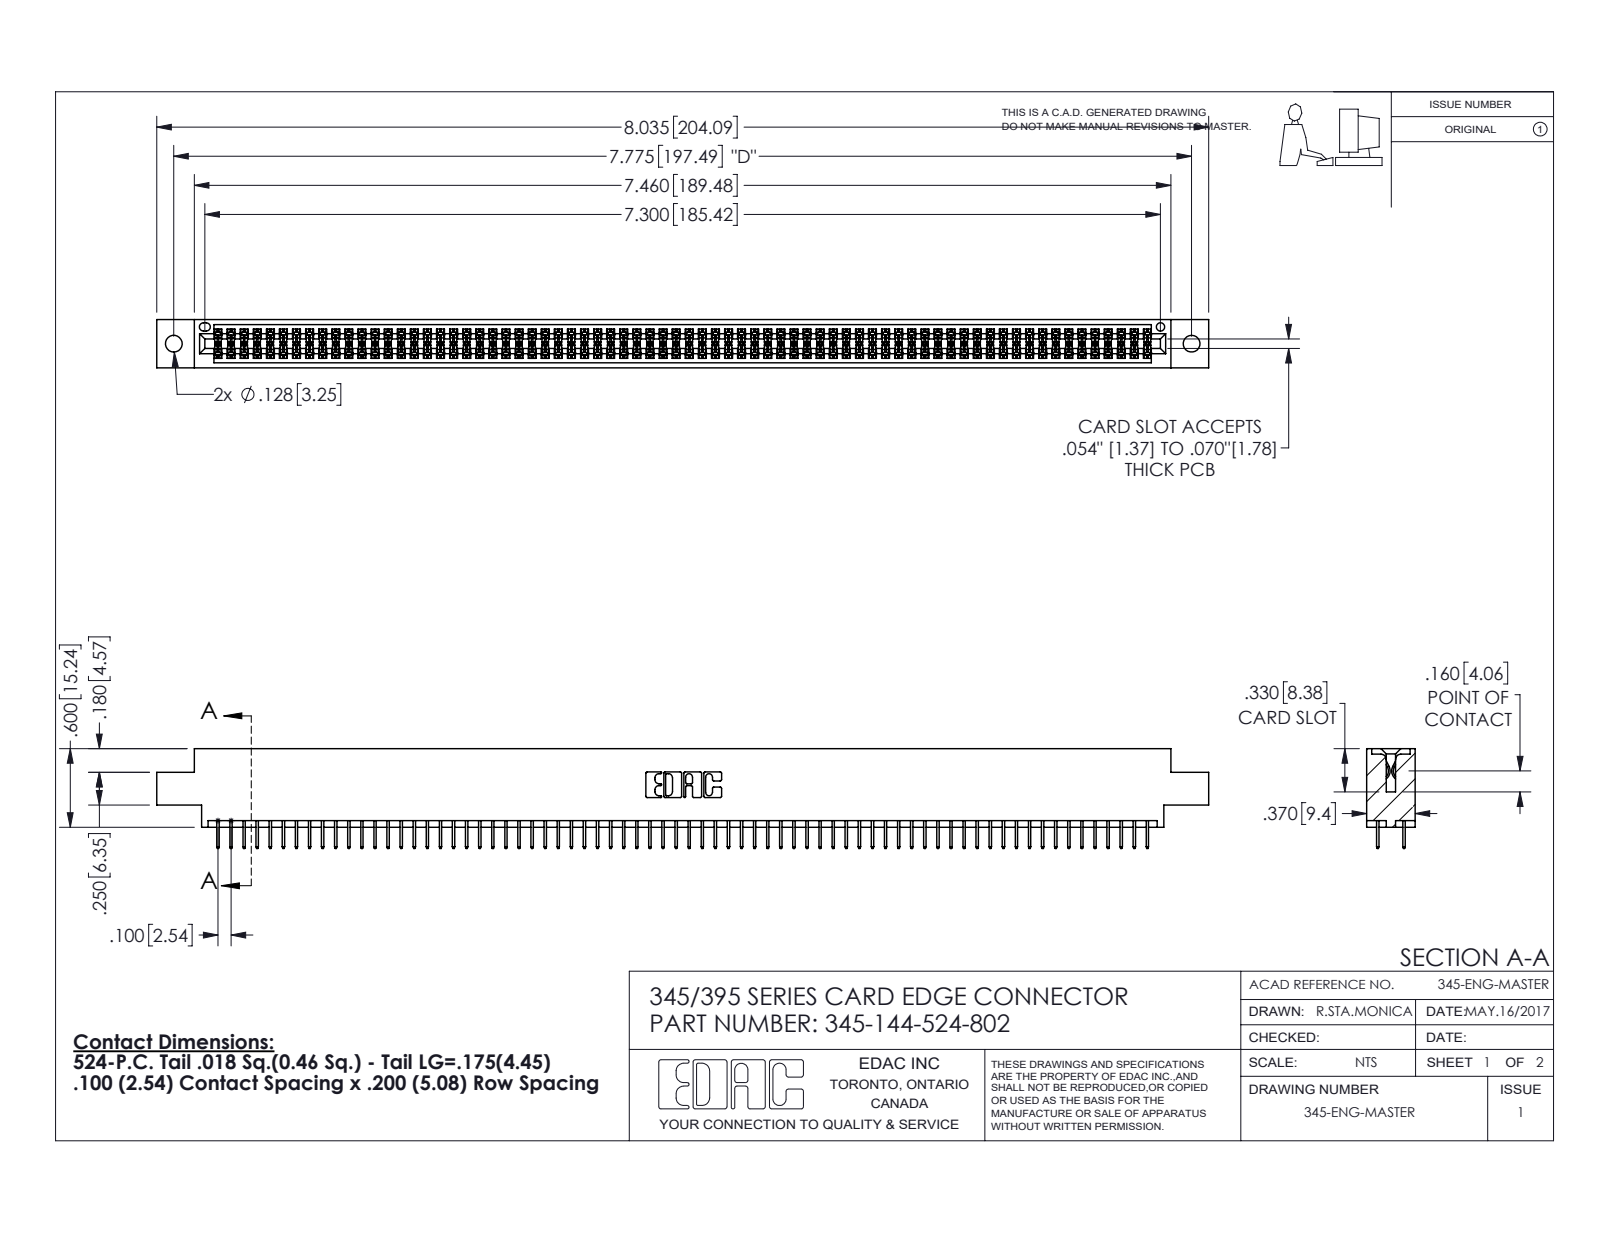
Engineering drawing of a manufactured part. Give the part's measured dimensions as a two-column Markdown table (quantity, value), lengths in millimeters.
| quantity | value |
| --- | --- |
| part name | 345-292-001_345-293-124; 345 Part_0.170 Offset - 0.128 Dia; 345-144-524-802 |
| STEP written by | SolidWorks 2016 (CONFIG_CONTROL_DESIGN) |
| units | millimeters |
| bodies | 145 solids, 7906 faces (5700 planar, 2206 cylindrical, 0 other) |
| overall size | 204.1 × 19.4 × 9.4 |
| volume | 19 730 mm³ |
| surface area | 29 050 mm² |
| round holes (diameter × count) | 3.3 × 2, 1.6 × 1 |
| partial cylindrical surfaces (radius × count) | 0.2 × 216, 0.3 × 22, 0.2 × 6, 0.8 × 6, 0.7 × 3, 0.4 × 2, 0.5 × 2, 0.6 × 2 |
| main face-to-face distances | 1.8, 7.6, 5.1, 9.4, 2.5, 6.9, 0.6, 5.7, 1.8, 4.4 |
| hole center spacings | 6.9, 191.5, 197.5 |
